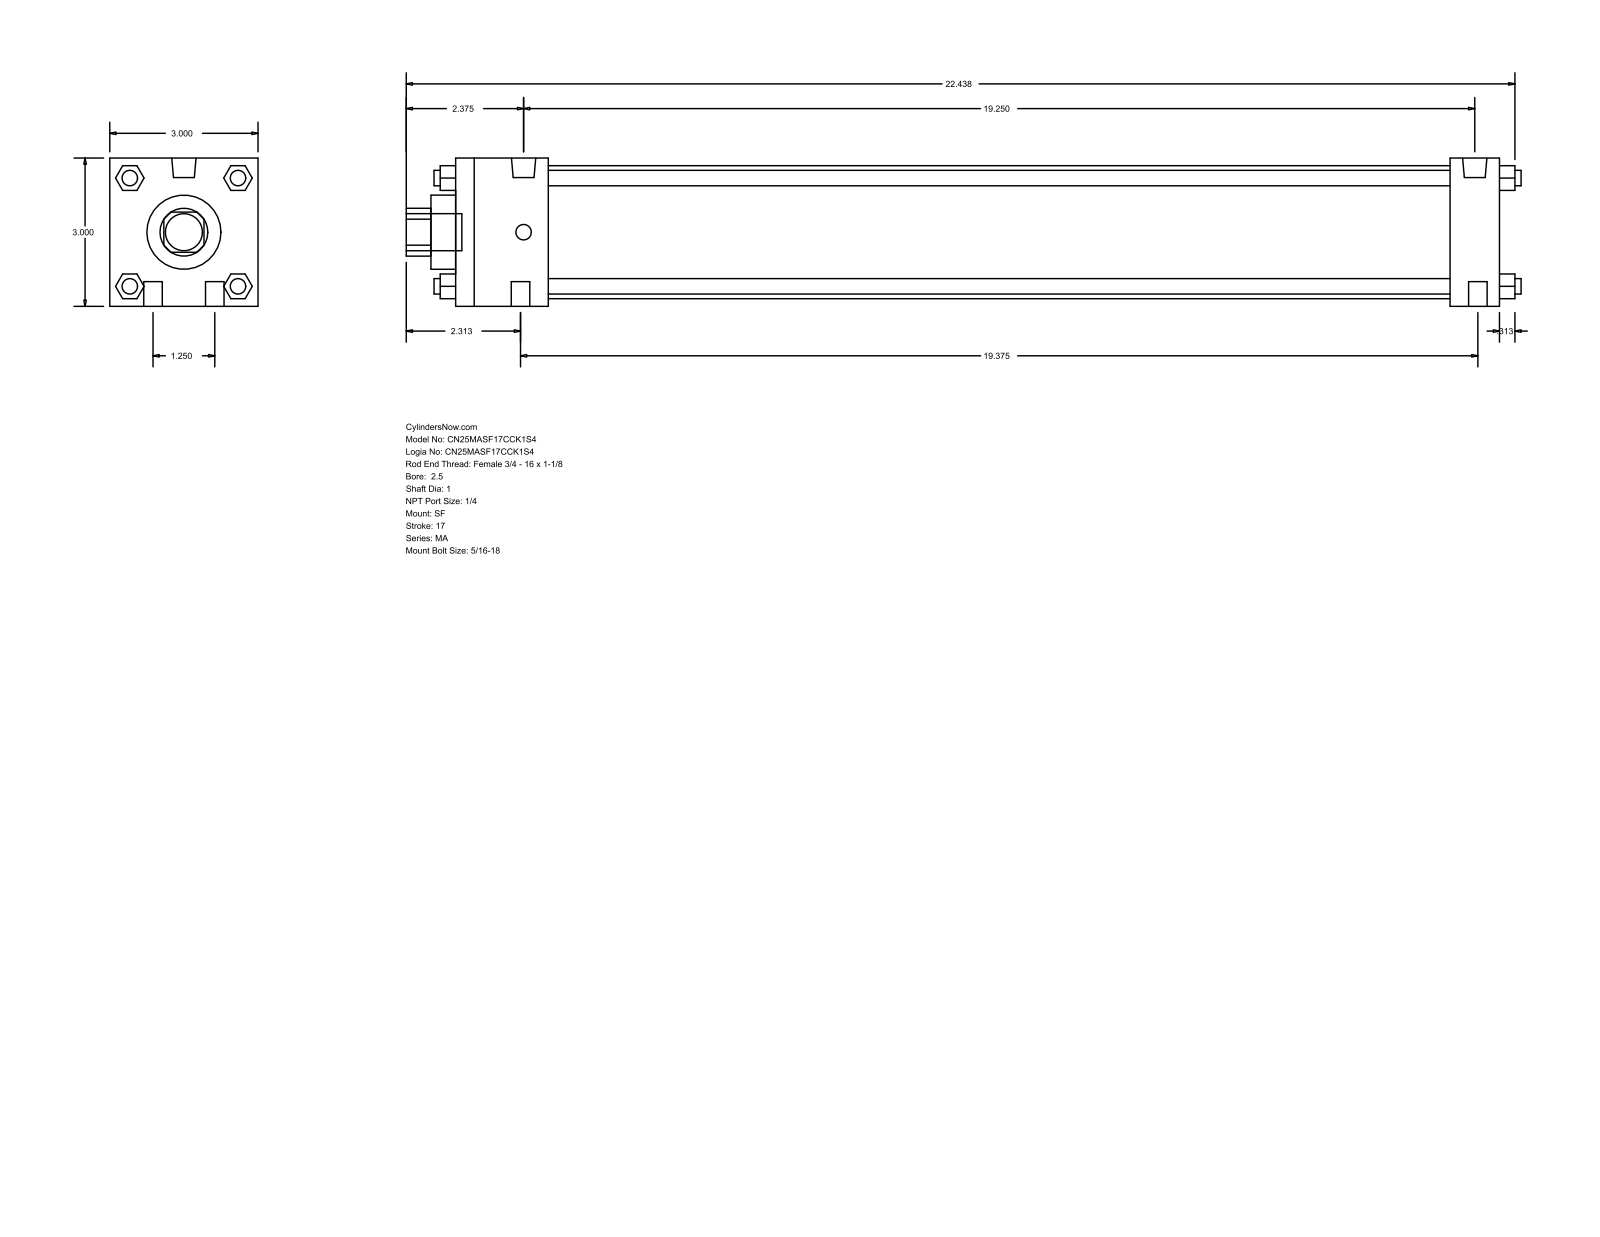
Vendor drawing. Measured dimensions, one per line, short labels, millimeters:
name: MA_SF__0250_1
written by: GSSL Pune (CONFIG_CONTROL_DESIGN)
unit: mm
bodies: 0 solids, 124 faces (94 planar, 30 cylindrical, 0 other)
size: 573.09 × 76.2 × 76.2
holes: 1× ⌀25.4, 1× ⌀38.1, 1× ⌀68.33
bosses: 6× ⌀7.94, 4× ⌀9.53, 2× ⌀12.49, 1× ⌀19.05
rounds: 1× R12.29
face distances: 76.2, 536.58, 12.7, 25.4, 511.18, 47.63, 463.55, 488.95, 27.81, 48.17
